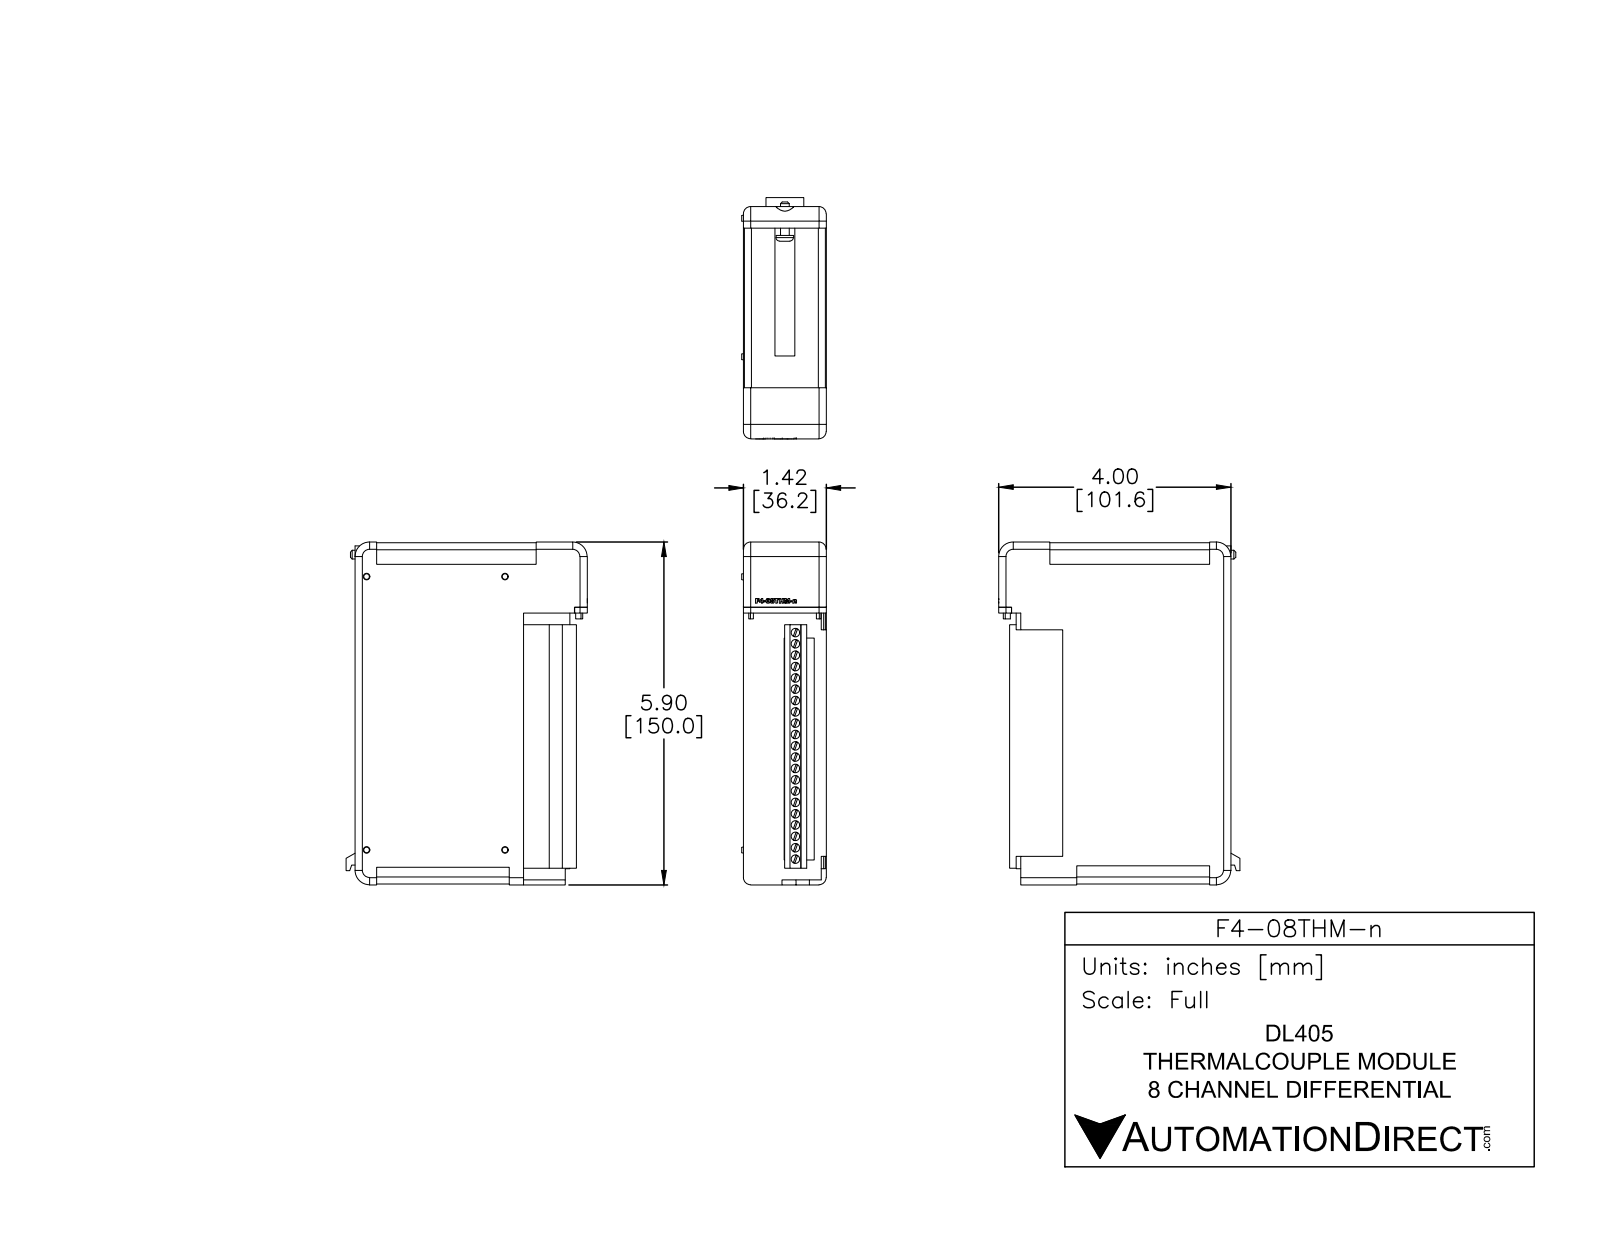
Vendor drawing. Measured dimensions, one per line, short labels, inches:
name: F4-08THM-k
written by: SolidWorks 2014 (AUTOMOTIVE_DESIGN)
unit: in
bodies: 13 solids, 470 faces (345 planar, 77 cylindrical, 48 other)
size: 5.905 × 4.156 × 1.455
volume: 25.81 in³; area: 102.3 in²
holes: 21× ⌀0.148
bosses: 1× ⌀0.3, 1× ⌀0.15
rounds: 8× R0.125, 4× R0.12, 3× R0.25, 2× R0.015, 2× R0.03, 1× R0.151, 1× R0.171
face distances: 1.425, 0.335, 1.09, 0.826, 0.264, 0.599, 0.1, 0.7, 2.9, 0.015
hole spacings: 0.585, 0.195, 0.78, 1.365, 1.17, 0.39, 1.95, 0.39
